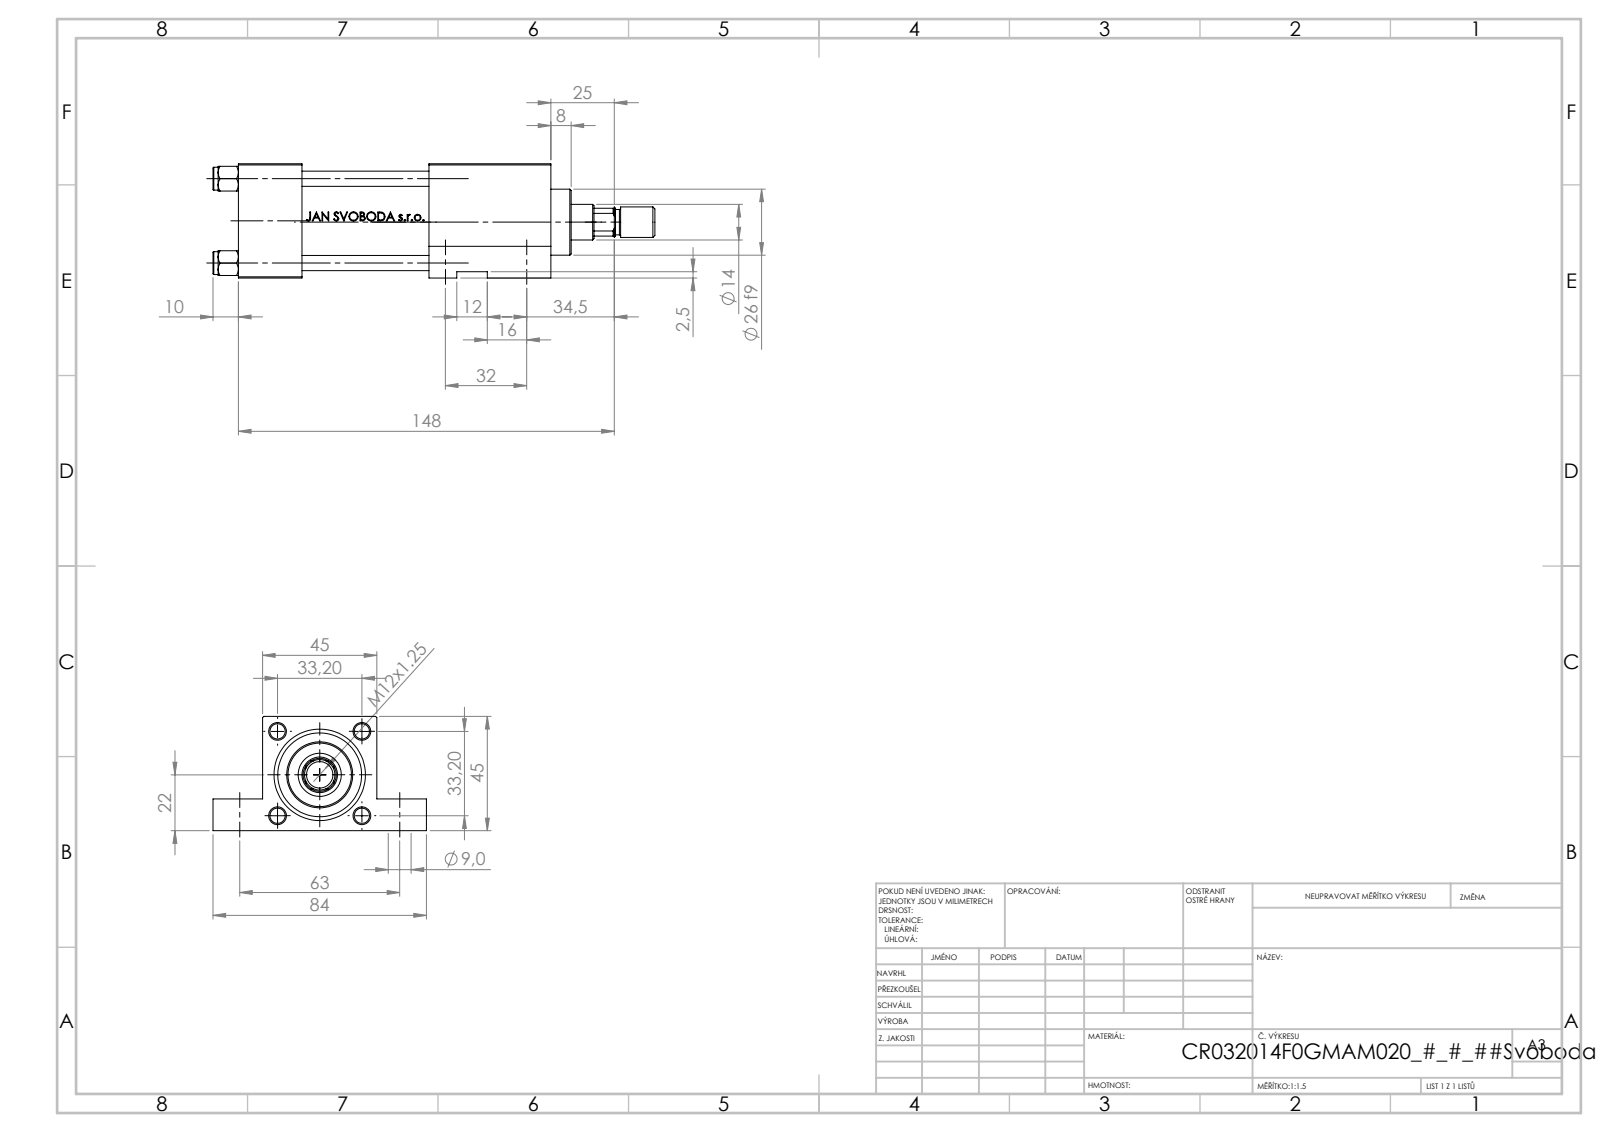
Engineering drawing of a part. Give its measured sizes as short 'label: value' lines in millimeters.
name: V215CR_F_Body; ROD_END_AH; V215_VC_A; V215CR_VCP_F (+2 more)
written by: SolidWorks 2019 (CONFIG_CONTROL_DESIGN)
unit: mm
bodies: 12 solids, 1116 faces (440 planar, 130 cylindrical, 546 other)
size: 174 × 84 × 45
volume: 213 643 mm³; area: 73 564 mm²
holes: 4× ⌀6, 4× ⌀9, 2× ⌀7, 2× ⌀20, 1× ⌀6.5, 1× ⌀13, 1× ⌀13.16, 1× ⌀14, 1× ⌀17, 1× ⌀24, 1× ⌀32, 1× ⌀33
bosses: 4× ⌀9, 1× ⌀38, 1× ⌀26, 1× ⌀12, 1× ⌀10
rounds: 1× R6.5
face distances: 45, 25, 98, 123, 50, 32.5, 75, 48, 12.5, 10
hole spacings: 33.2, 23.13, 23.83, 32, 46.95, 63, 70.66, 75.5
